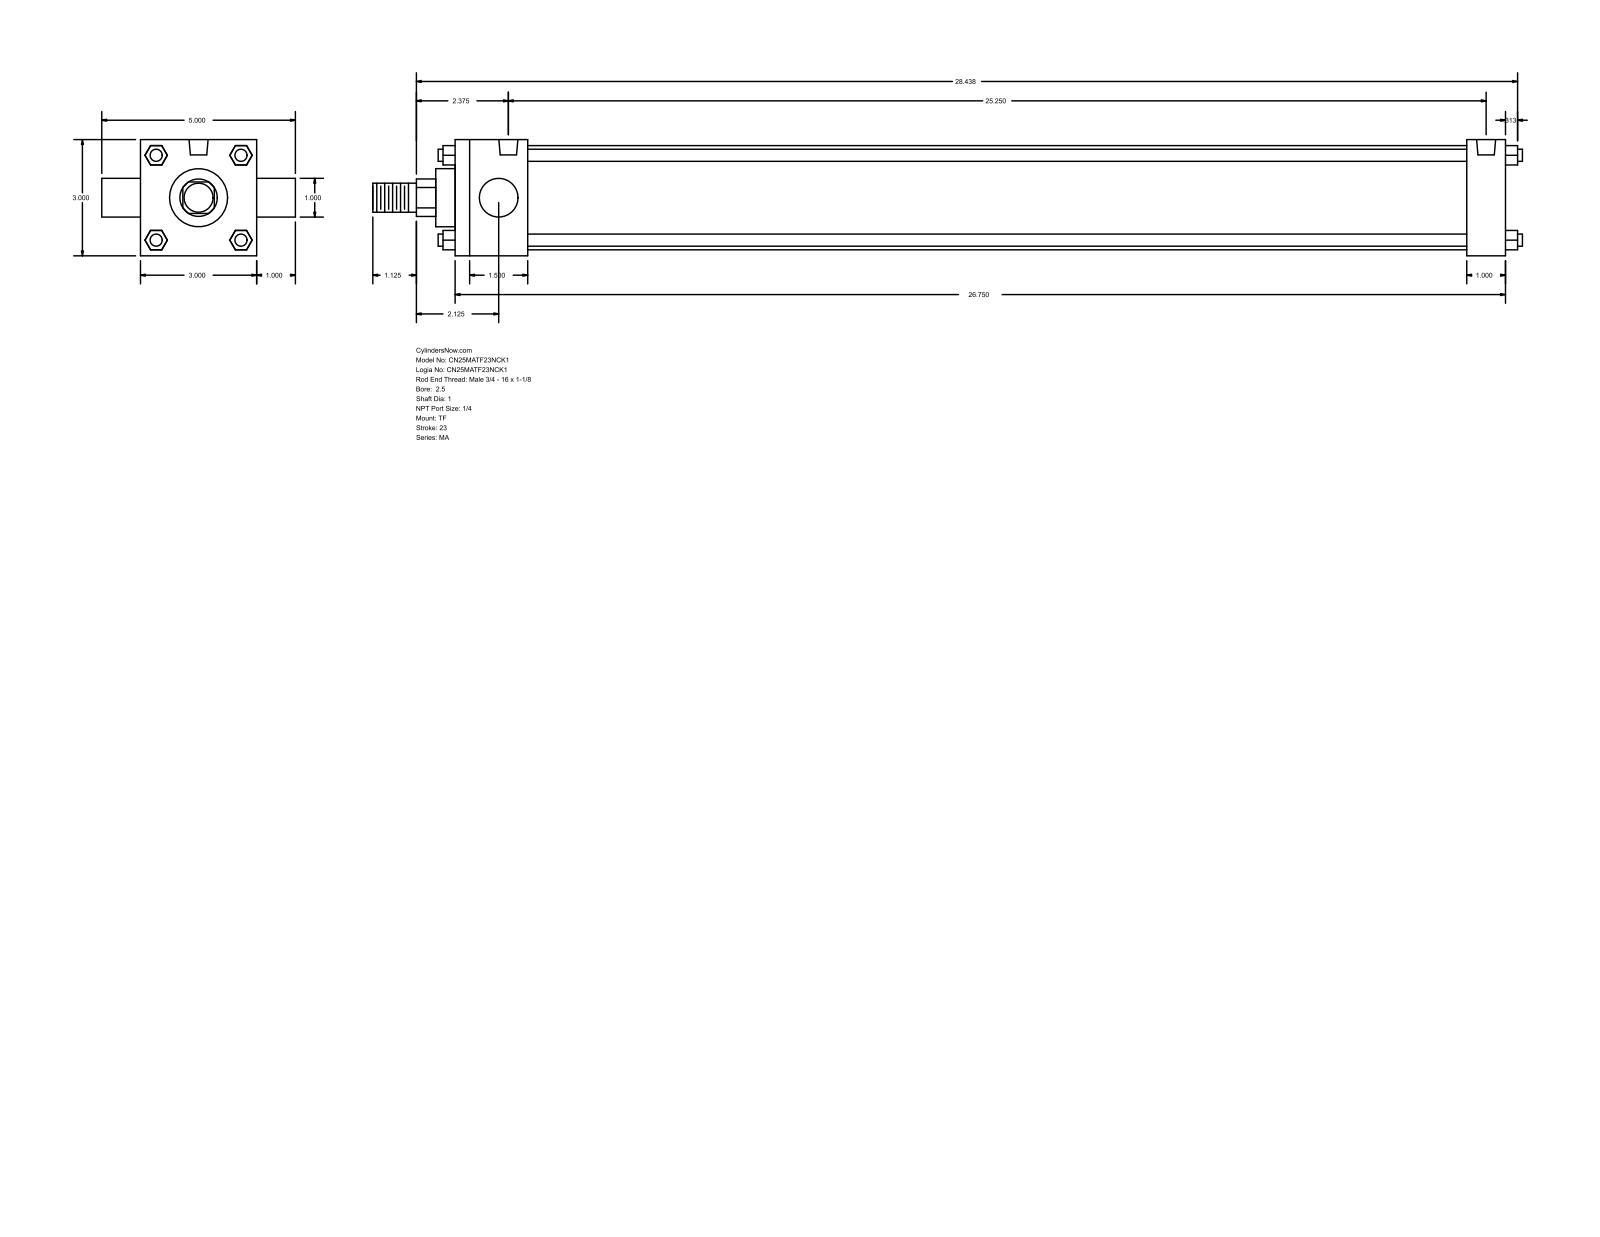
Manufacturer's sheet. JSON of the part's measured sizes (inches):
{"part_name": "MA_TF__0250_1", "step_written_by": "GSSL Pune (CONFIG_CONTROL_DESIGN)", "units": "inches", "bodies": {"solids": 0, "faces": 120, "planar": 92, "cylindrical": 28, "other": 0}, "overall_size": [29.687, 5, 3], "round_holes": [[0.313, 3], [0.492, 2]], "round_bosses_or_shafts": [[0.313, 4], [1, 2], [2.69, 1], [1.5, 1], [0.75, 1]], "partial_cylinders_radius": [[0.484, 1]], "face_to_face_distances": [3, 27.125, 1, 0.5, 1.875, 26.125, 24.25, 25.25, 4, 1.095], "hole_center_spacings": [25.25]}
